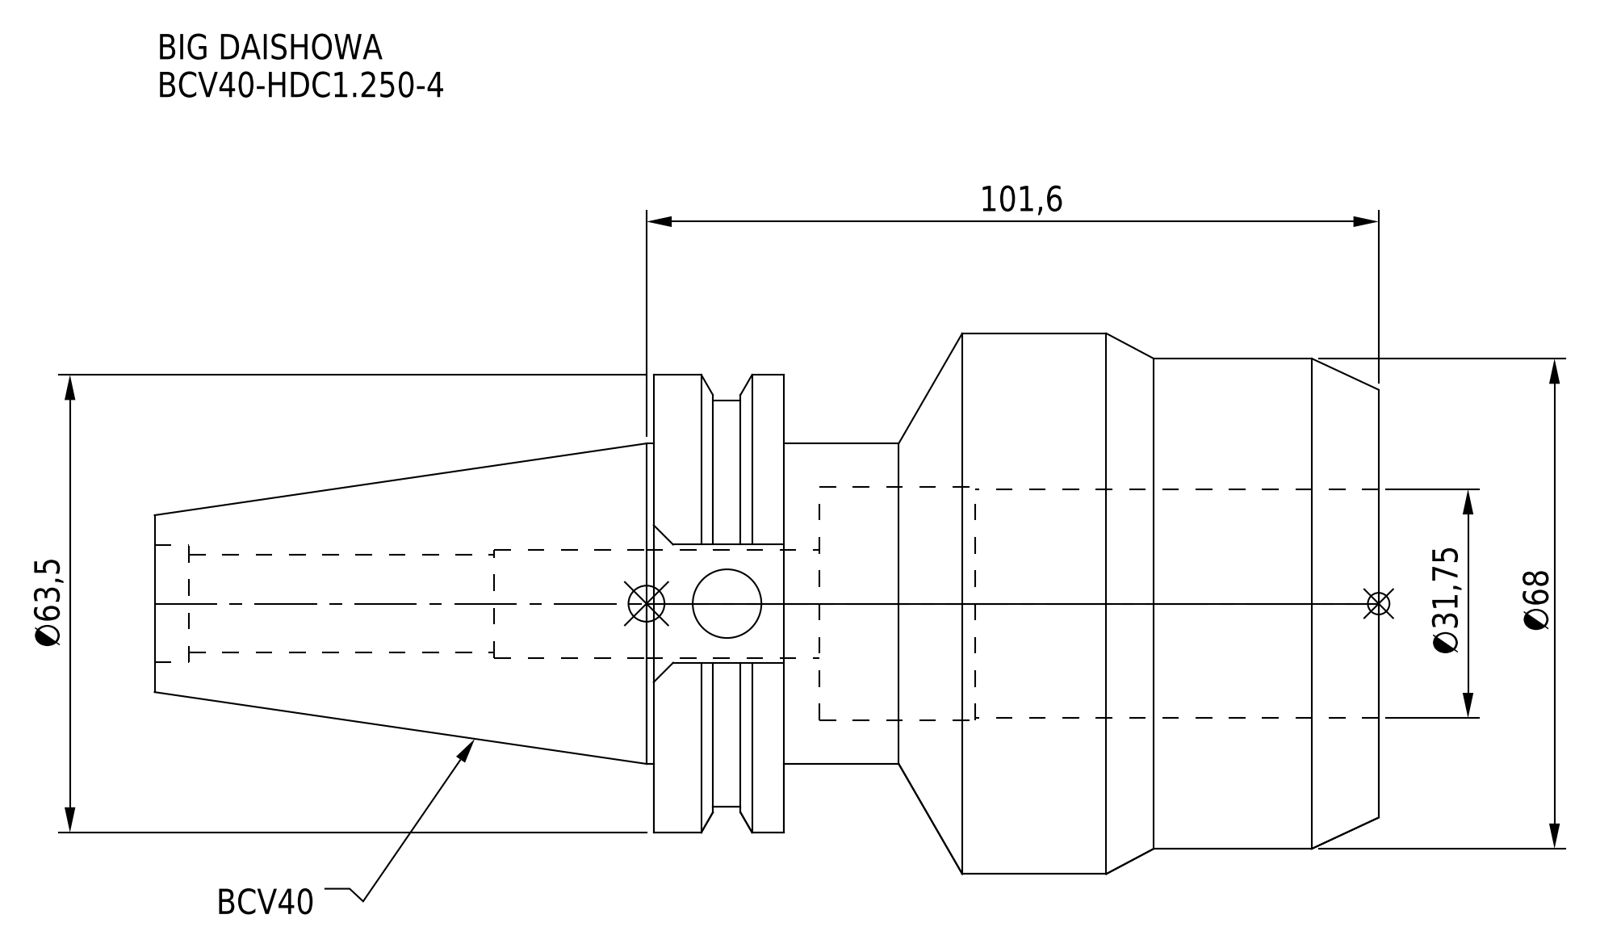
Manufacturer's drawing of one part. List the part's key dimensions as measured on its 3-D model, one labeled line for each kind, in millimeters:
Part name (STEP PRODUCT): BCV40-HDC1_250-4
STEP written by: CREO PARAMETRIC BY PTC INC, 2016380 (AUTOMOTIVE_DESIGN)
Units: millimetres
Bodies: 1 solid, 63 faces (23 planar, 28 cylindrical, 12 other)
Overall size (bounding box): 169.85 × 75 × 75
Volume: 313 624 mm³ · Surface area: 48 565 mm²
Round holes (diameter × count): ⌀9.53 ×1, ⌀13.6 ×1, ⌀15 ×1, ⌀16.32 ×1, ⌀31.75 ×1, ⌀32.3 ×1
Round bosses / shafts (diameter × count): ⌀75 ×1, ⌀68 ×1, ⌀63.5 ×1, ⌀56.36 ×1, ⌀44.45 ×1
Main face-to-face distances: 82.55, 100.6, 18.05, 77.6, 4.95, 23, 169.85, 92.25, 87.3, 69.25
